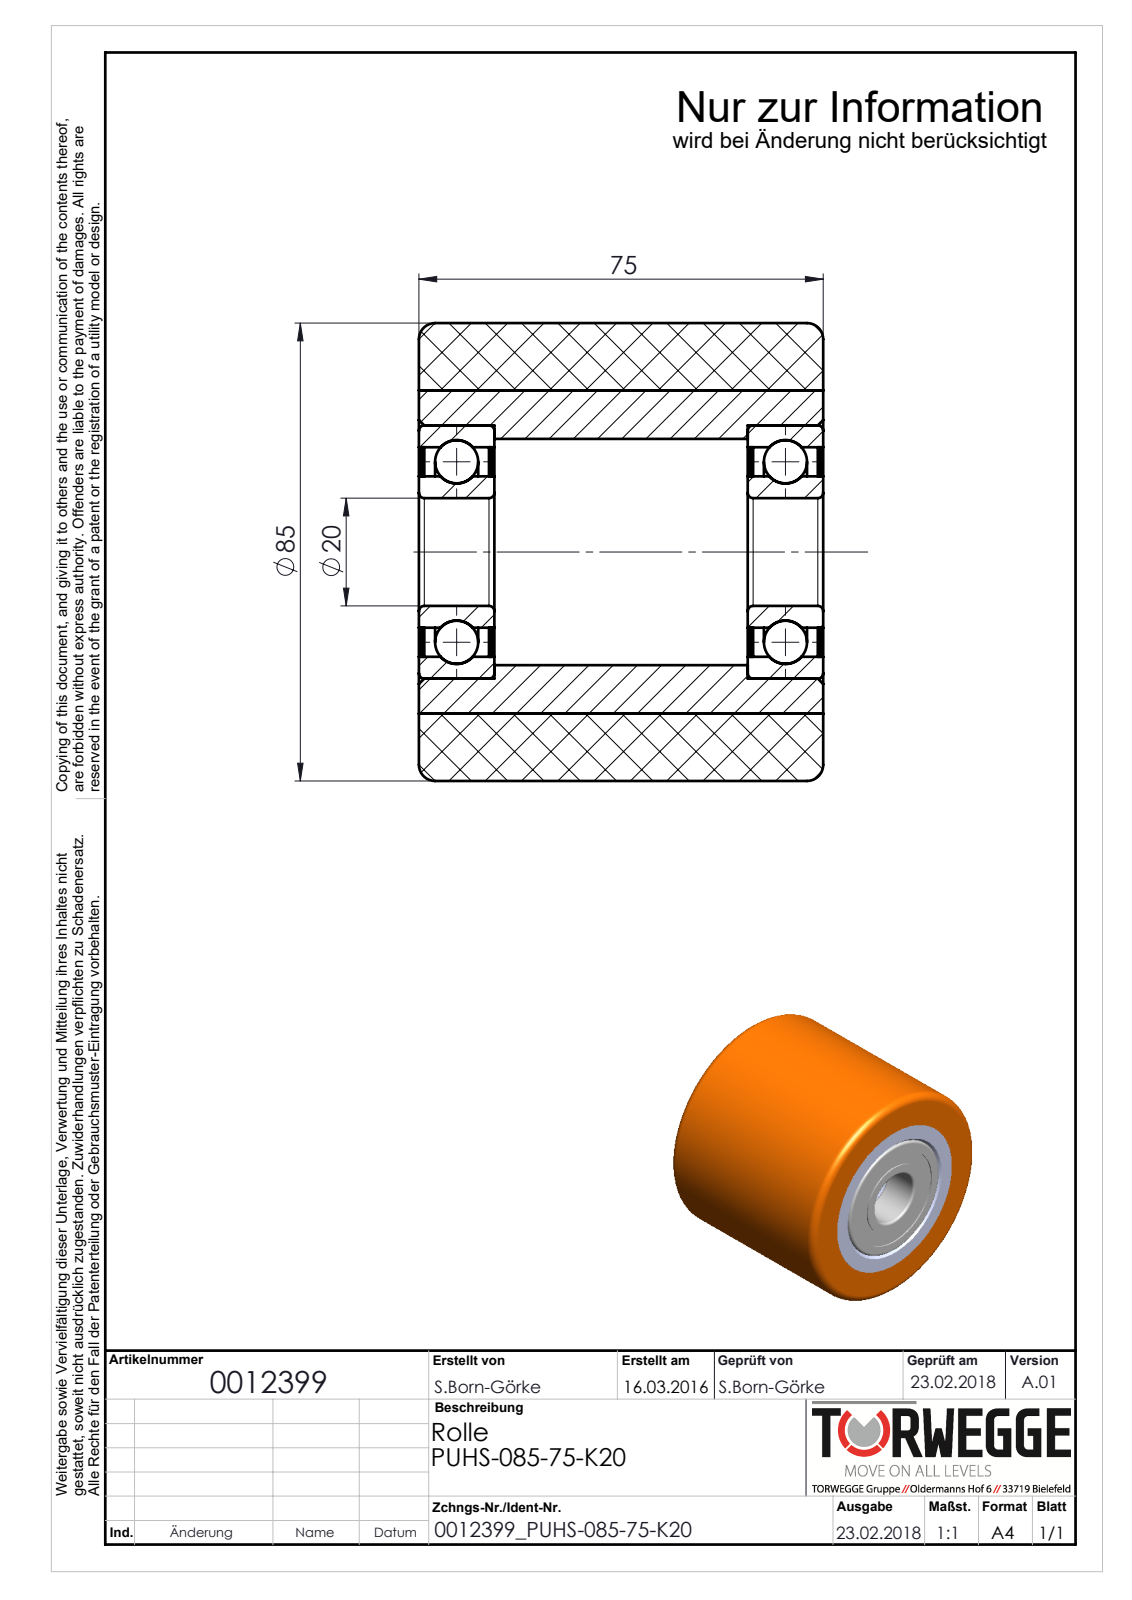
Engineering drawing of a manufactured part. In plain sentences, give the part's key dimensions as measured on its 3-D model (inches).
The part is named "0012399_PUHS-085-75-K20". Its 3-D file was written by "SolidWorks 2016 (AUTOMOTIVE_DESIGN)". It is 12 solids with 118 faces: 22 planar, 52 cylindrical and 44 other. Overall it measures 3.346 by 3.346 by 2.953 inches. Its volume is 20.97 cubic inches and its surface area 142.3 square inches. Round holes: 1 of diameter 0.787, 1 of diameter 1.106, 1 of diameter 1.531, 1 of diameter 1.654, 1 of diameter 1.85, 1 of diameter 2.362. Round bosses or shafts: 1 of diameter 3.346. The main face-to-face distances are 0.02, 2.402, 2.953, 0.512, 0.039, 0.531, 2.421, 0.492, 2.382, 0.551.
